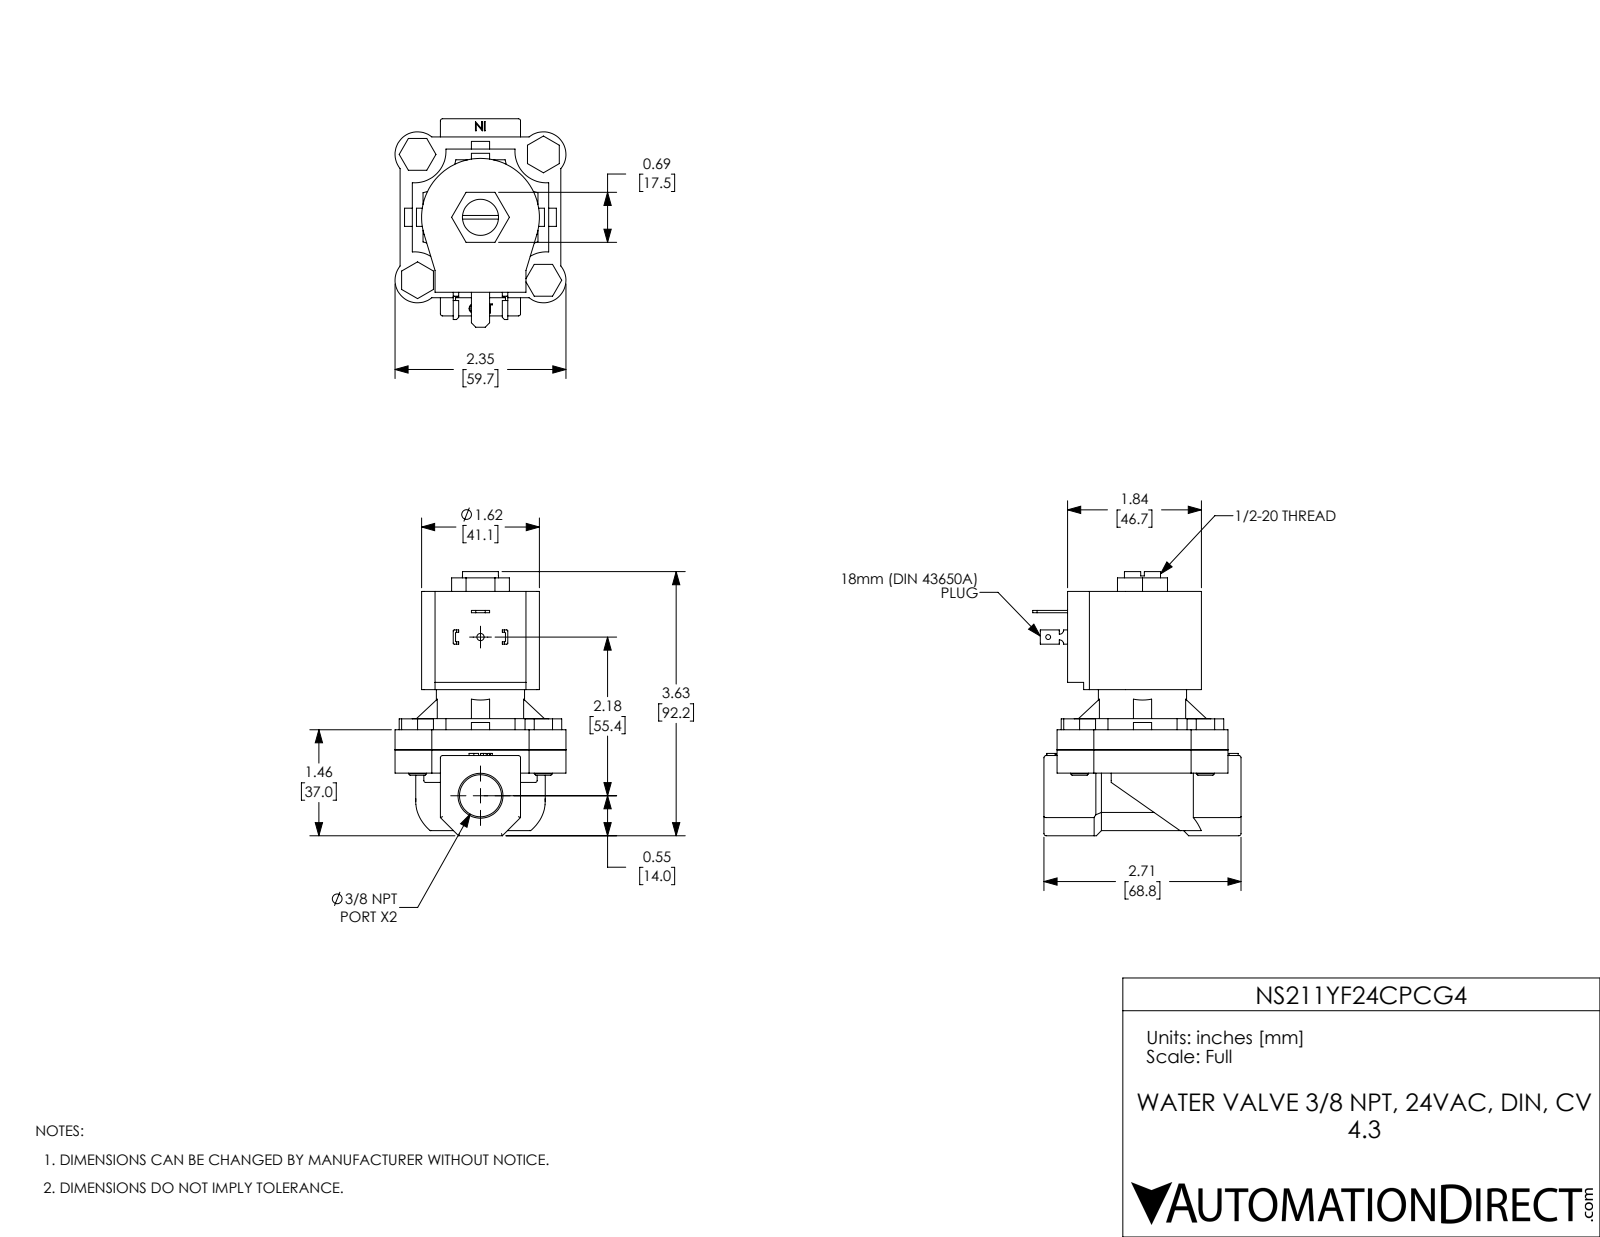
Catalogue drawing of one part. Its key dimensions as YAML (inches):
part_name: "NS211YF24CPCG4"
step_written_by: "SolidWorks 2021 (CONFIG_CONTROL_DESIGN)"
units: inches
bodies: {solids: 11, faces: 383, planar: 237, cylindrical: 113, other: 33}
overall_size: [3.63, 2.865, 2.35]
volume: 9.675
surface_area: 64.2
round_holes:
  - {diameter: 0.25, count: 4}
  - {diameter: 0.067, count: 1}
  - {diameter: 0.1, count: 1}
  - {diameter: 0.496, count: 1}
  - {diameter: 0.512, count: 1}
  - {diameter: 0.578, count: 1}
  - {diameter: 1.155, count: 1}
round_bosses_or_shafts:
  - {diameter: 0.248, count: 4}
  - {diameter: 1.213, count: 1}
partial_cylinders:
  - {radius: 0.03, count: 15}
  - {radius: 0.015, count: 8}
  - {radius: 0.31, count: 4}
  - {radius: 0.432, count: 4}
  - {radius: 0.579, count: 4}
  - {radius: 0.06, count: 2}
  - {radius: 0.81, count: 1}
  - {radius: 0.89, count: 1}
face_to_face_distances: [0.276, 2.177, 1.901, 0.32, 0.596, 2.497, 0.554, 1.656, 0.25, 1.147]
hole_center_spacings: [1.223, 1.73, 2.446, 2.181]
